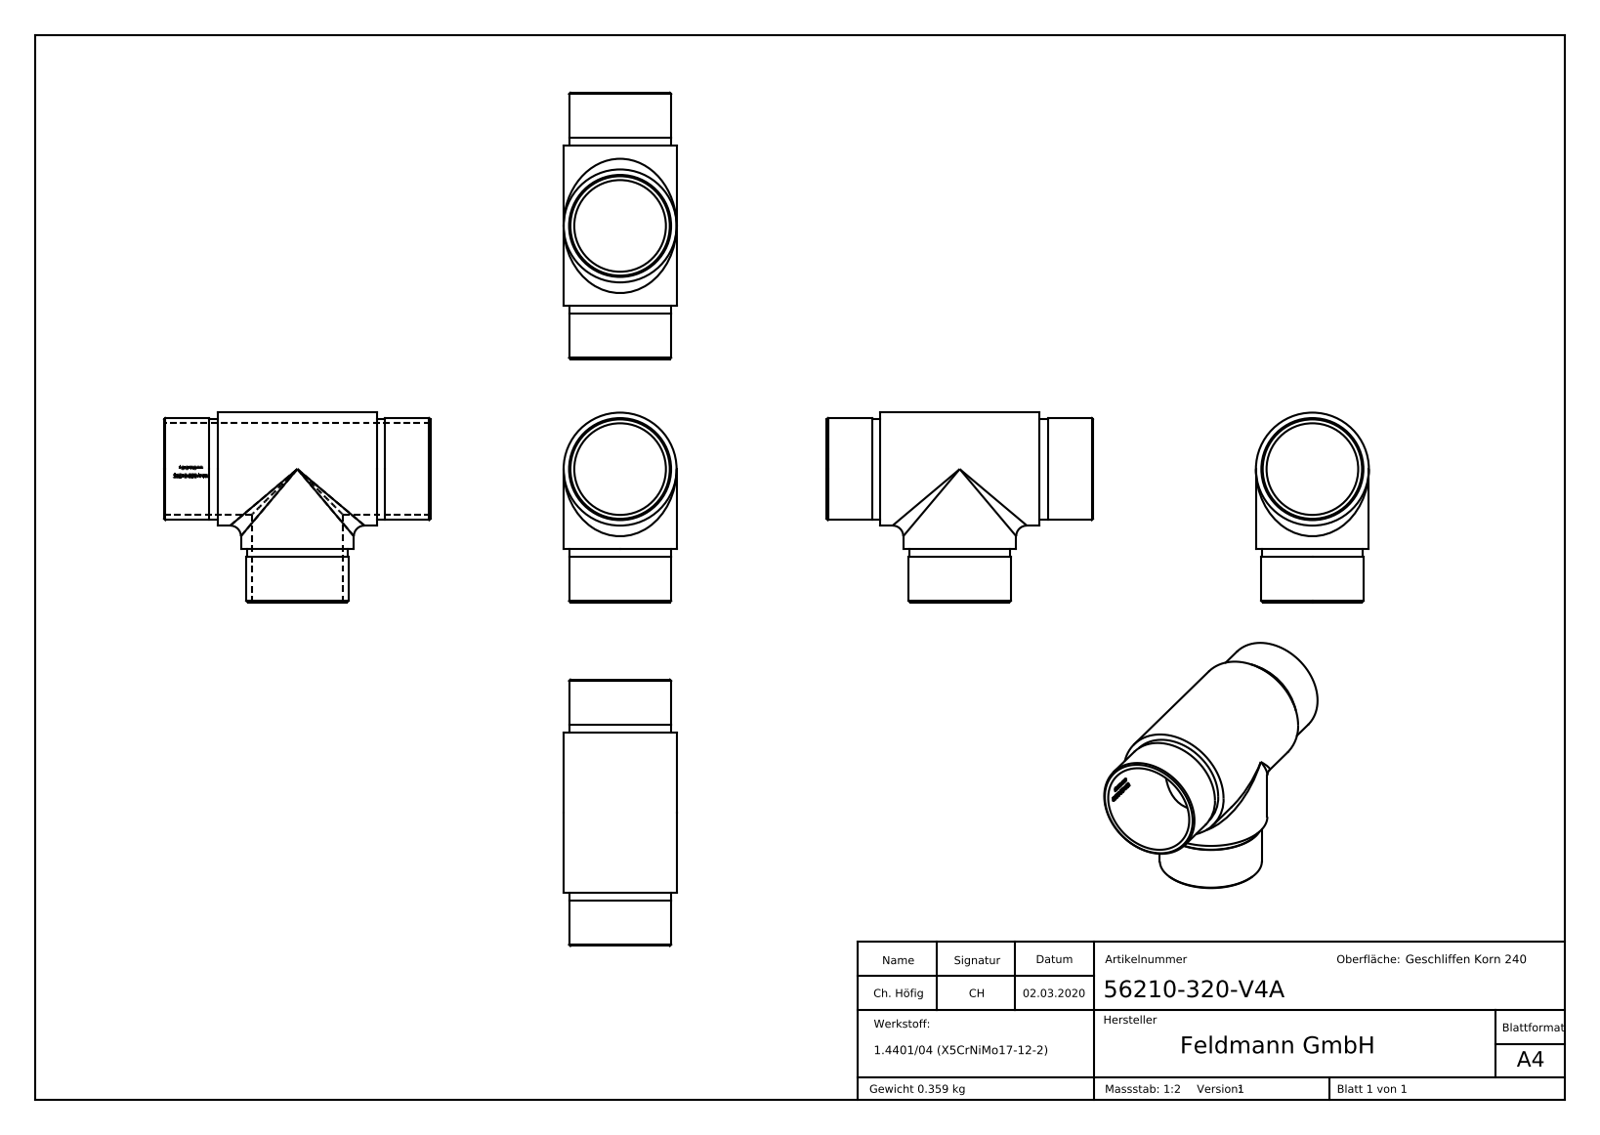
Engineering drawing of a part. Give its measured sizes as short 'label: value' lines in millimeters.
name: 56210-320-V4A
written by: SolidWorks 2015 (CONFIG_CONTROL_DESIGN)
unit: mm
bodies: 1 solid, 285 faces (132 planar, 39 cylindrical, 114 other)
size: 100 × 71.2 × 42.4
volume: 44 873 mm³; area: 30 859 mm²
holes: 2× ⌀34.4
bosses: 2× ⌀42.4, 2× ⌀38.3, 2× ⌀37.9
rounds: 1× R17.3
face distances: 20, 80, 60, 100, 17, 3, 83, 63, 66, 0.74
